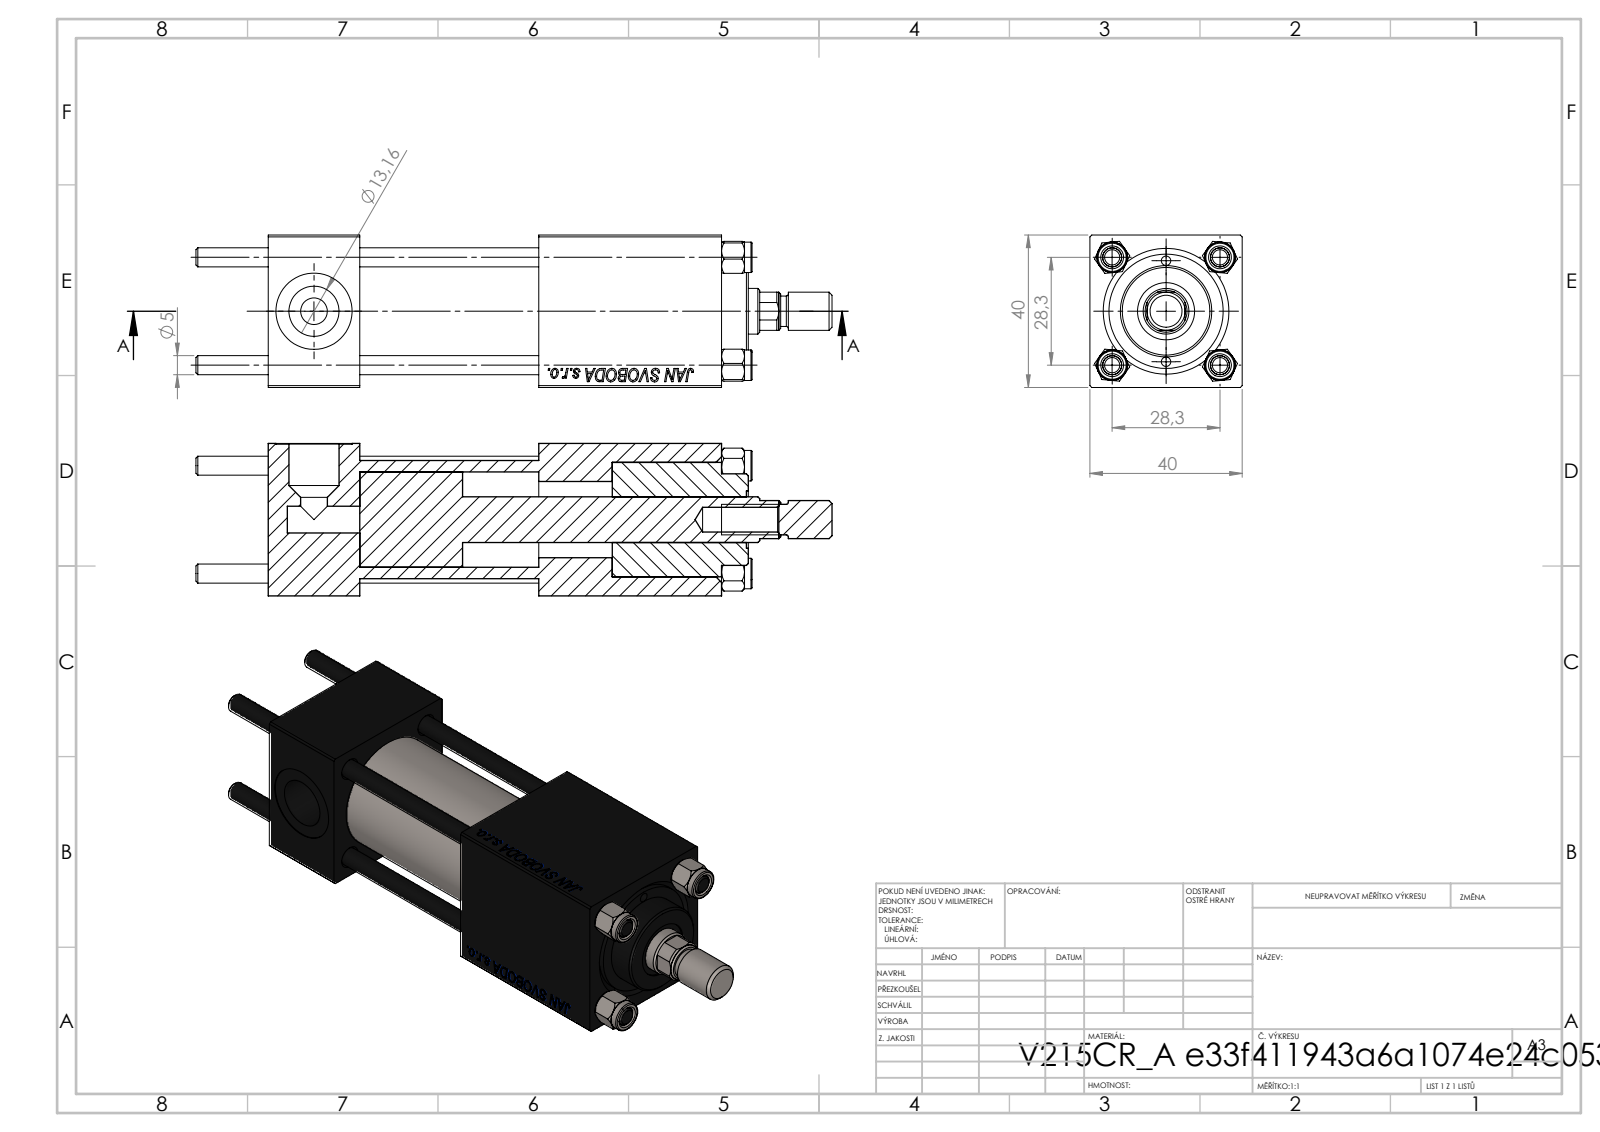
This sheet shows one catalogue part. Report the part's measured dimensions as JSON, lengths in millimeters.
{"part_name": "NUT_M5; V215CR_VCP; CR025_012_A_0_G_A_G_M_020_+#_##_TYCINKA; V215CR_BODY_A (+2 more)", "step_written_by": "SolidWorks 2019 (CONFIG_CONTROL_DESIGN)", "units": "millimeters", "bodies": {"solids": 12, "faces": 1152, "planar": 523, "cylindrical": 87, "other": 542}, "overall_size": [167, 40, 40], "volume_mm3": 145725, "surface_area_mm2": 59562, "round_holes": [[5, 4], [20, 3], [2.5, 2], [7, 2], [13.16, 2], [6.5, 1], [12, 1], [15, 1], [25, 1], [30, 1]], "round_bosses_or_shafts": [[8, 5], [31, 1], [24, 1], [10, 1]], "partial_cylinders_radius": [[5.5, 1]], "face_to_face_distances": [40, 24, 90.3, 66.3, 119, 95, 28.7, 71, 47, 19.3], "hole_center_spacings": [14.18, 20.01, 28.3, 30.84, 13.25, 40.02, 26.5]}
